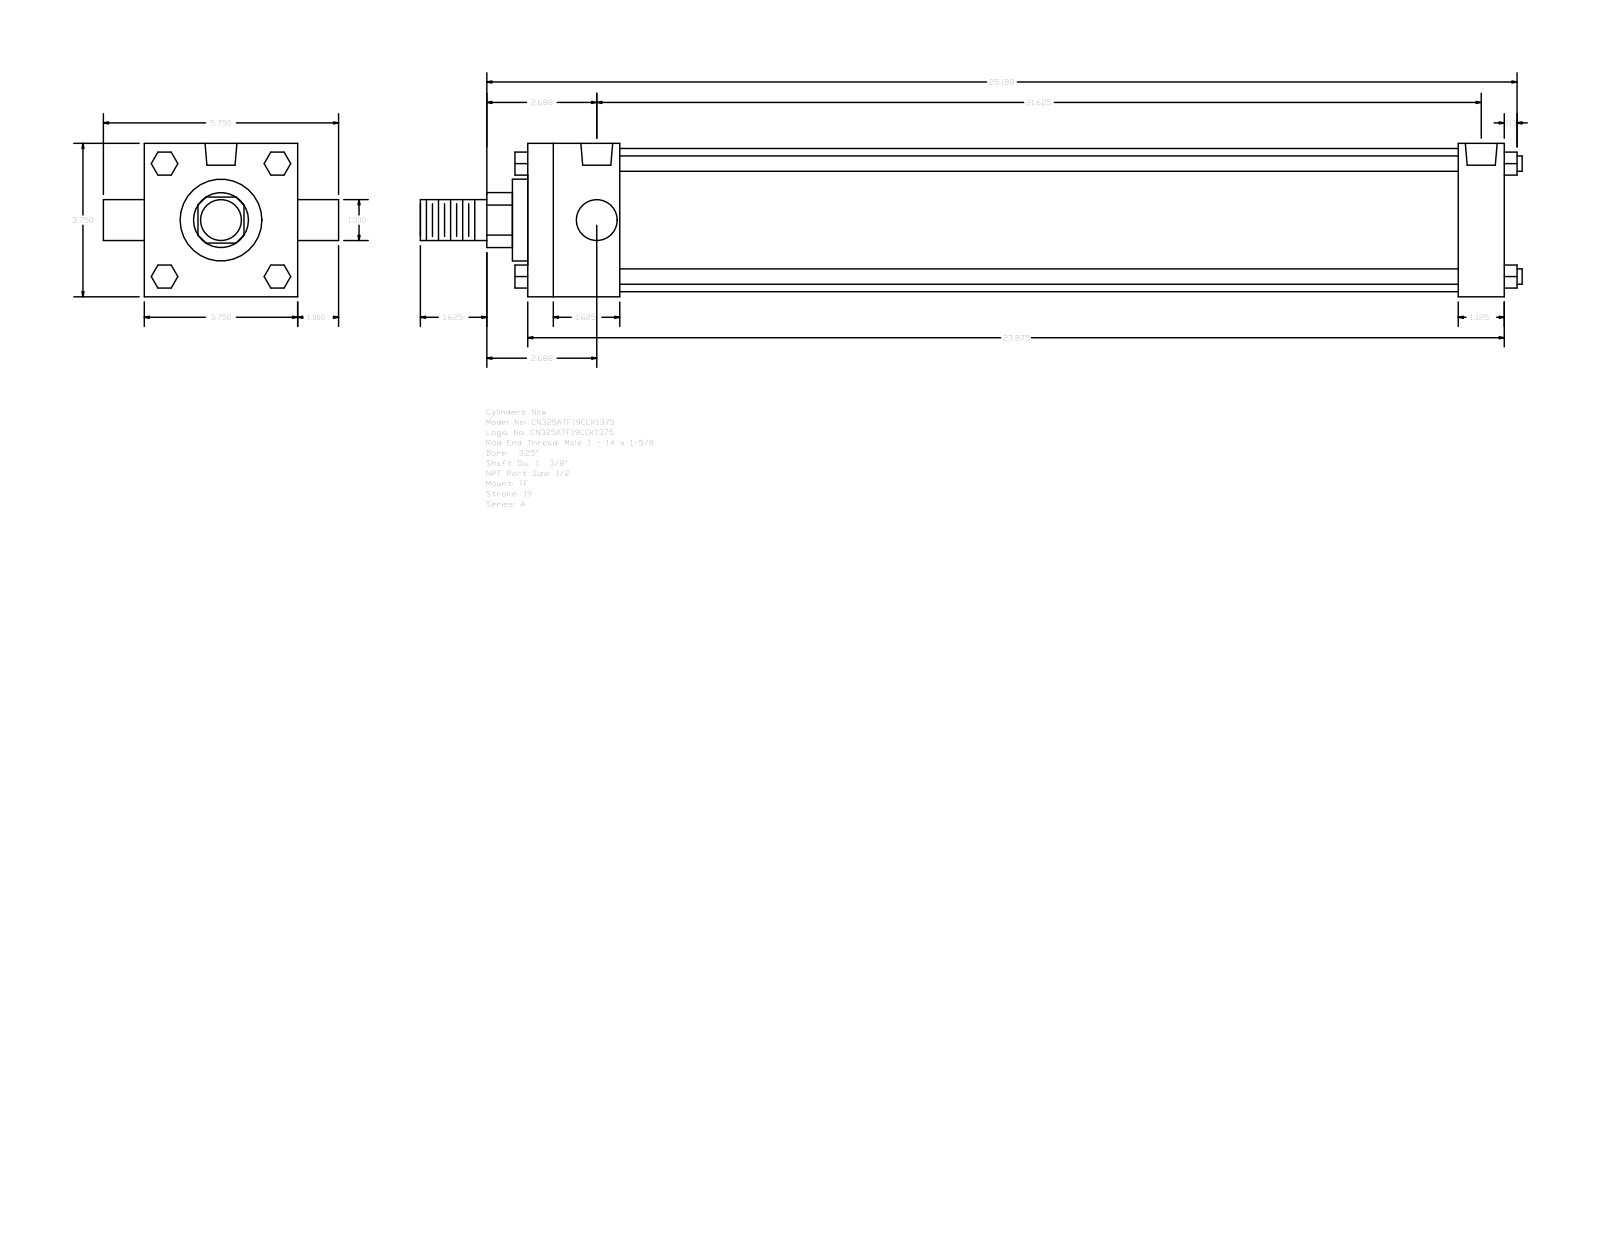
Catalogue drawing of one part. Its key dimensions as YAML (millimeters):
part_name: "A_TF__0325_1.375"
step_written_by: "GSSL Pune (CONFIG_CONTROL_DESIGN)"
units: millimeters
bodies: {solids: 0, faces: 120, planar: 92, cylindrical: 28, other: 0}
overall_size: [684.21, 146.05, 95.25]
round_holes:
  - {diameter: 8.73, count: 3}
  - {diameter: 19.77, count: 2}
round_bosses_or_shafts:
  - {diameter: 9.53, count: 4}
  - {diameter: 25.4, count: 2}
  - {diameter: 88.9, count: 1}
  - {diameter: 50.8, count: 1}
  - {diameter: 34.92, count: 1}
partial_cylinders:
  - {radius: 17.06, count: 1}
face_to_face_distances: [95.24, 606.43, 57.15, 28.58, 577.85, 520.7, 549.28, 66.67, 9.52, 587.37]
hole_center_spacings: [3.18, 546.1, 542.92, 549.28]
